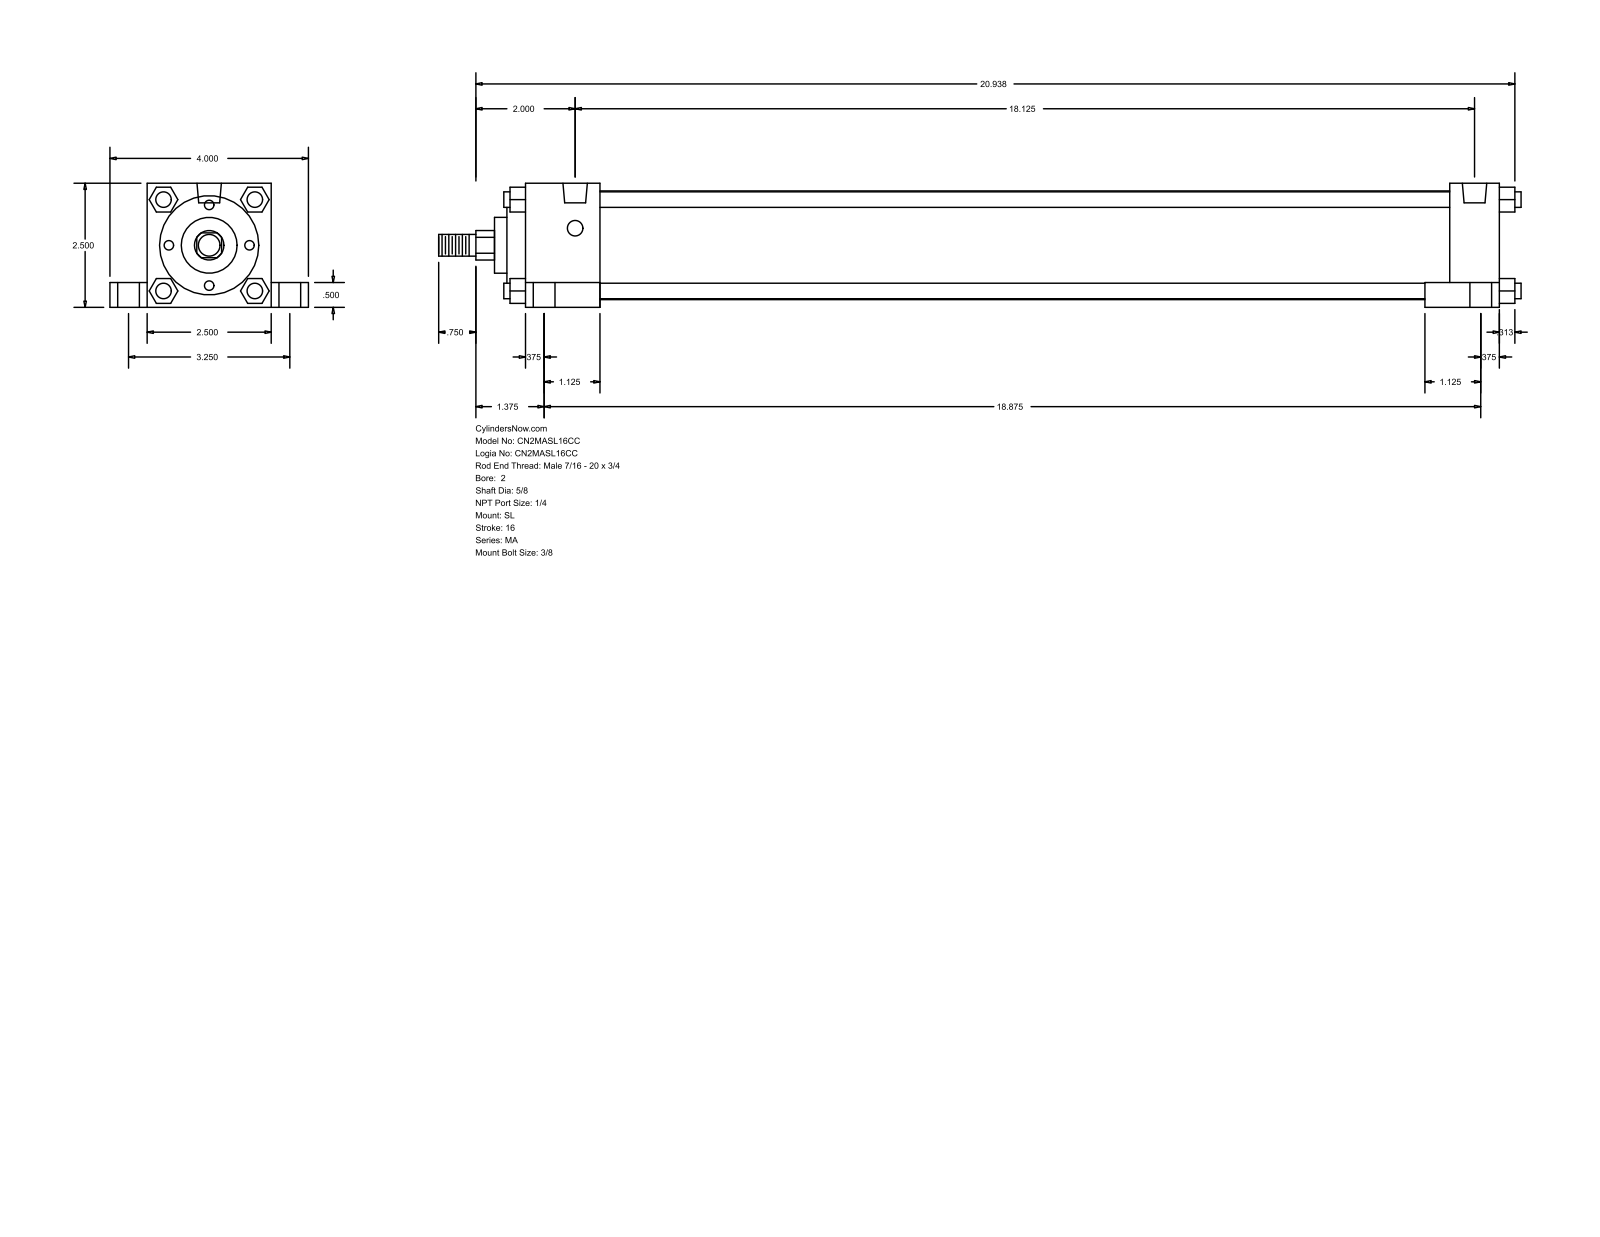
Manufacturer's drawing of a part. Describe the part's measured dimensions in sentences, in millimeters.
The part is named "MA_SL__0200_0.625". Its 3-D file was written by "GSSL Pune (CONFIG_CONTROL_DESIGN)". It is 0 solids with 150 faces: 113 planar, 37 cylindrical and 0 other. Overall it measures 554.04 by 101.6 by 63.5 millimeters. Round holes: 4 of diameter 7.94, 4 of diameter 11.11, 4 of diameter 17.46, 2 of diameter 12.49. Round bosses or shafts: 4 of diameter 7.94, 1 of diameter 55.63, 1 of diameter 50.8, 1 of diameter 28.57, 1 of diameter 15.88, 1 of diameter 11.11. Partial cylindrical surfaces (rounded edges, fillets, slot ends): 1 of radius 7.54. The main face-to-face distances are 63.5, 12.7, 9.52, 25.4, 19.05, 82.55, 38.1, 498.48, 50.8, 460.38. The hole center spacings are 41.39, 44.22, 82.54, 460.38, 465.38, 478.04, 479.43, 486.48.
